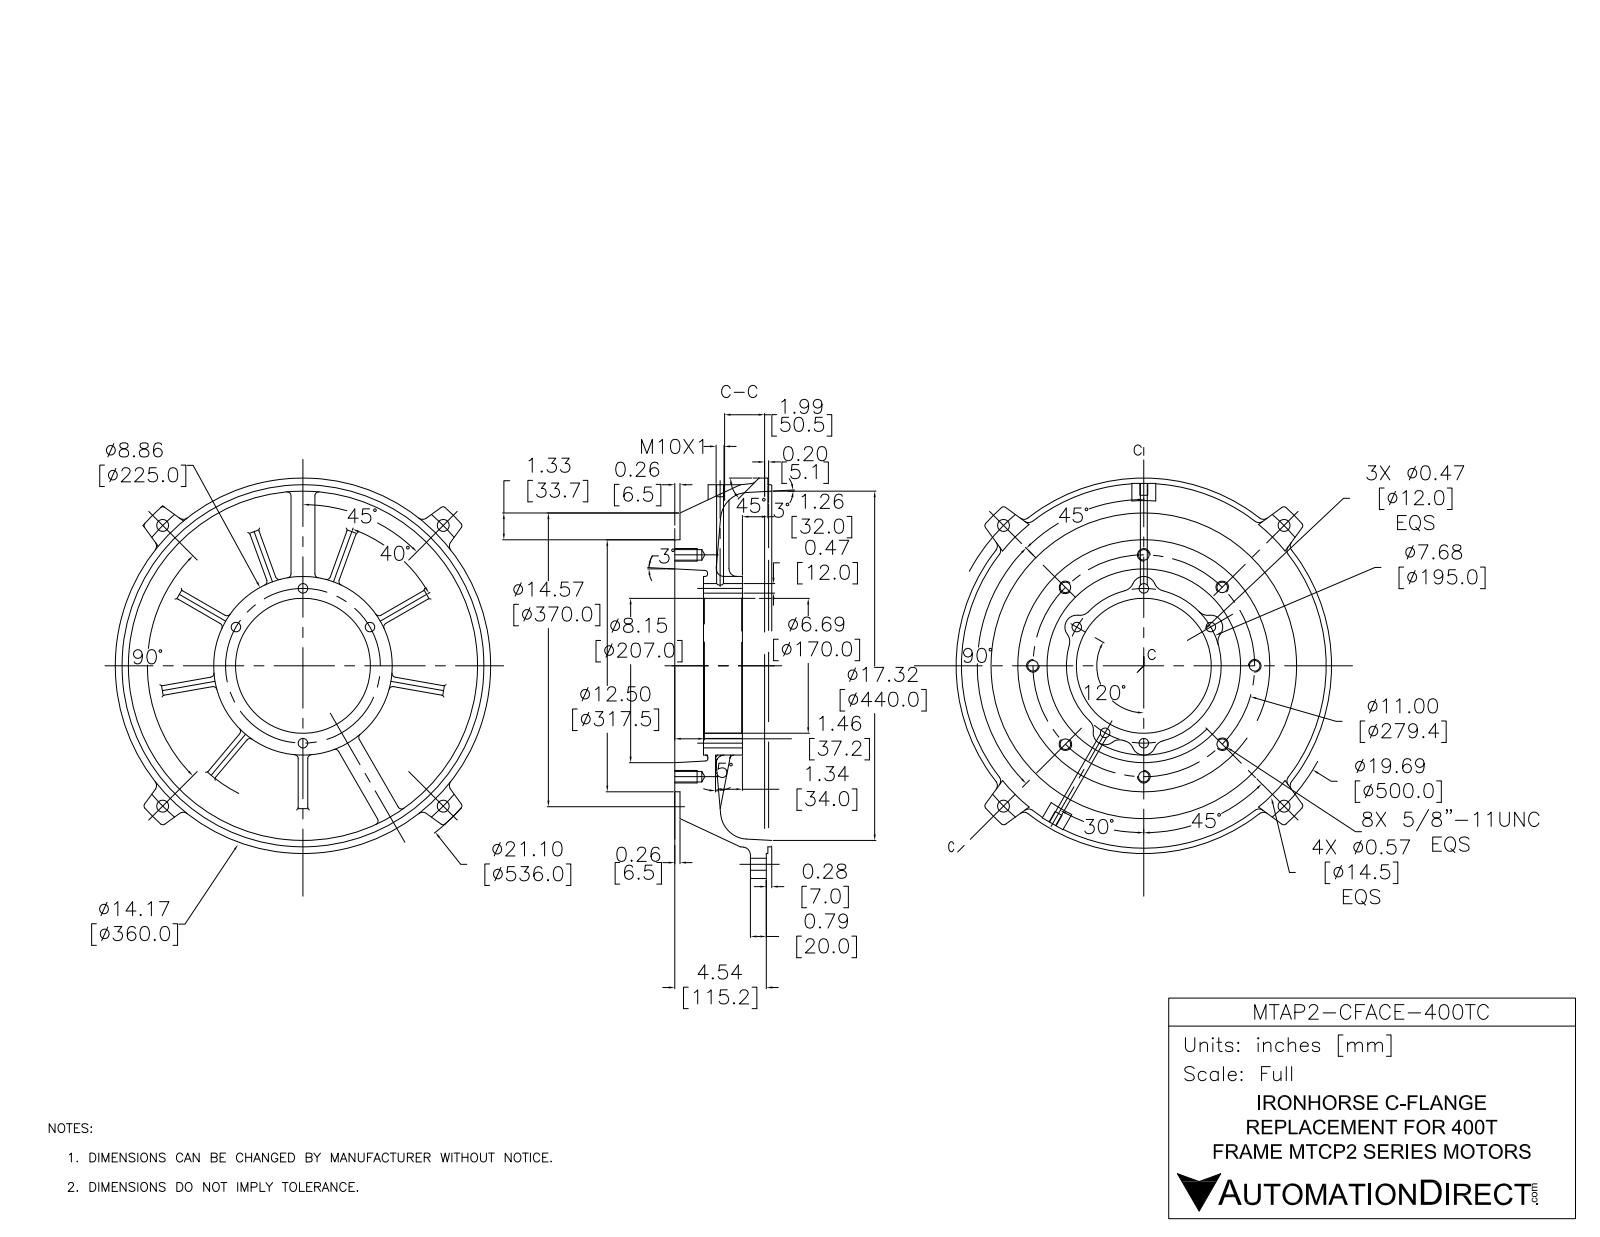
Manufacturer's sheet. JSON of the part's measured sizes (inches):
{"part_name": "MTAP2-CFACE-400TC", "step_written_by": "SolidWorks 2017 (AUTOMOTIVE_DESIGN)", "units": "inches", "bodies": {"solids": 2, "faces": 343, "planar": 53, "cylindrical": 196, "other": 94}, "overall_size": [21.023, 21.023, 4.783], "volume_in3": 517.4, "surface_area_in2": 1106, "round_holes": [[0.394, 8], [0.512, 8], [0.472, 5], [0.625, 1], [3.15, 1], [3.622, 1], [5.906, 1]], "round_bosses_or_shafts": [[18.622, 1], [17.953, 1], [12.5, 1], [8.858, 1], [6.693, 1]], "partial_cylinders_radius": [[0.591, 21], [0.197, 2], [1.969, 1], [2.461, 1], [3.839, 1], [10.551, 1]], "face_to_face_distances": [0.256, 1.248, 0.197, 3.023, 1.563, 1.307, 0.993, 0.315, 1.504, 4.587], "hole_center_spacings": [14.272, 3.839, 4.209, 5.5, 7.111, 10.163, 11.275, 3.889]}
